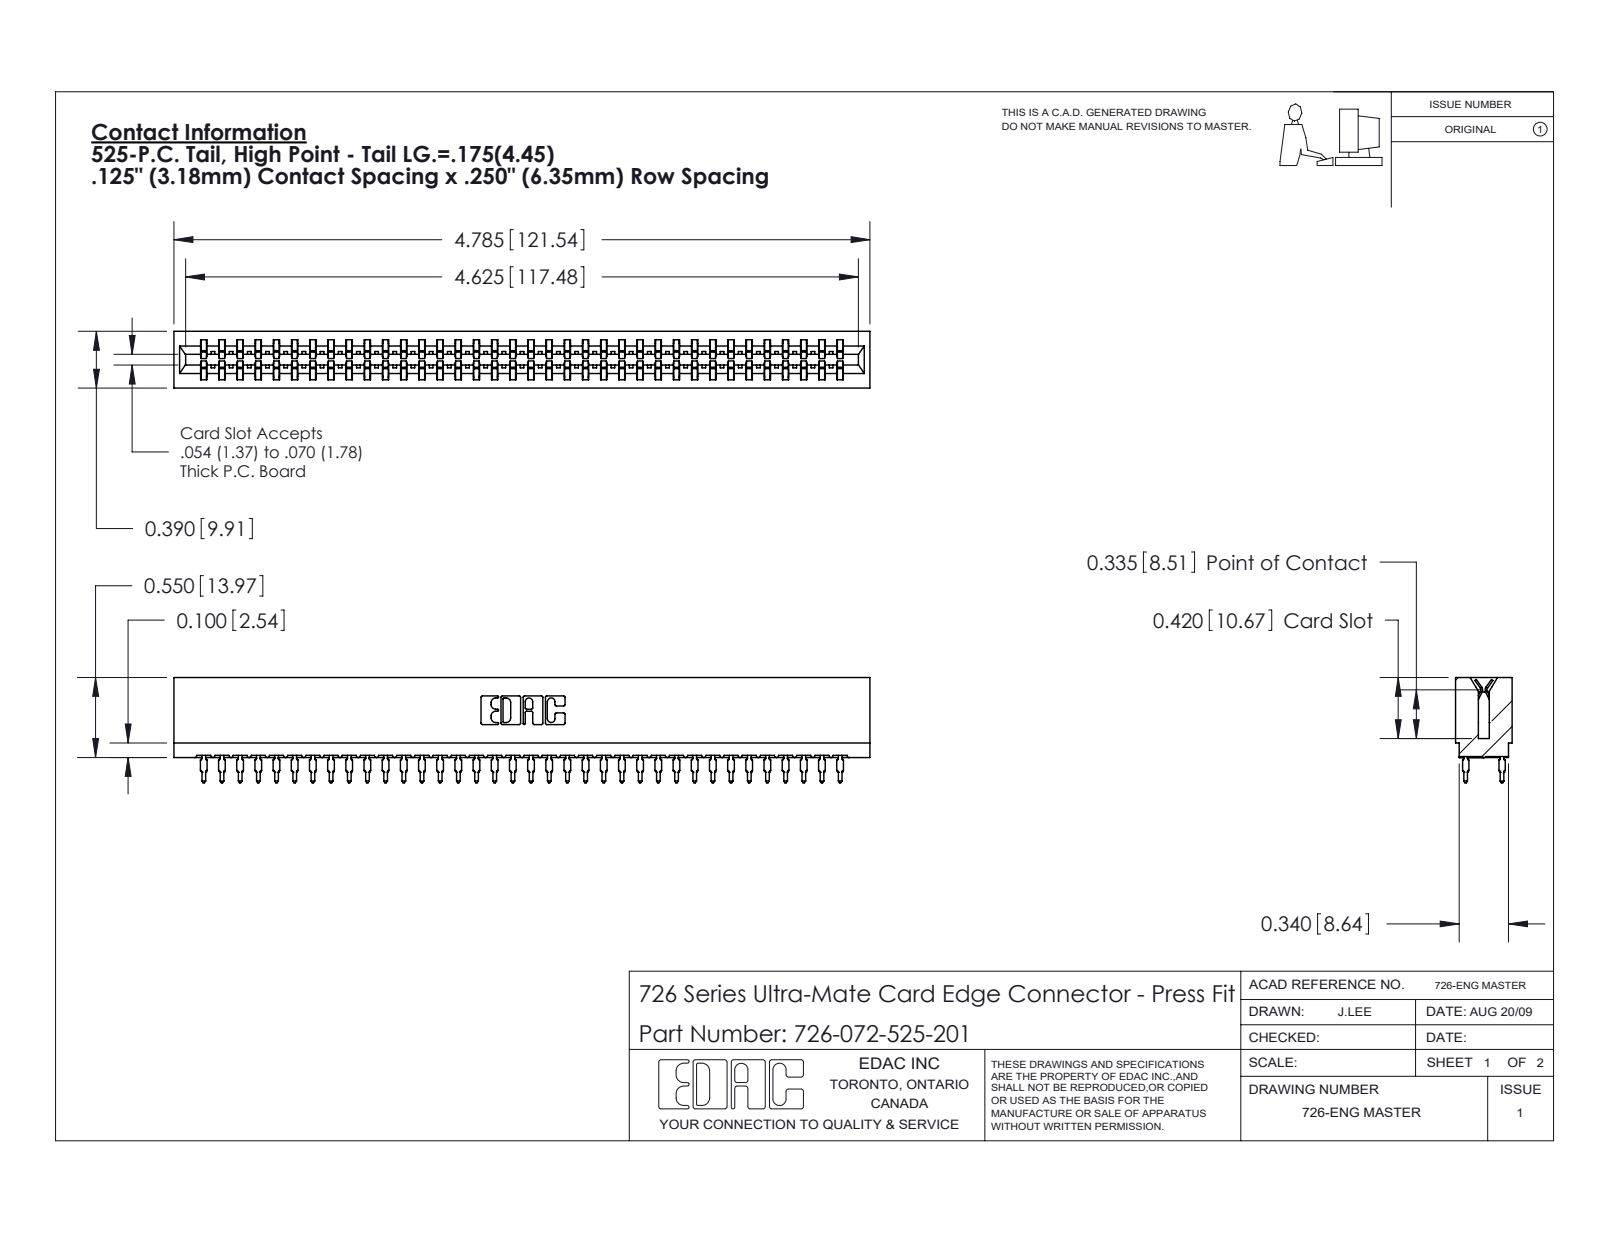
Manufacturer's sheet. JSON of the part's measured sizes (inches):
{"part_name": "726 Part_.515 Slot Depth - 01; 726-072-525-201; 746-292-001_525", "step_written_by": "SolidWorks 2020 (CONFIG_CONTROL_DESIGN)", "units": "inches", "bodies": {"solids": 73, "faces": 6541, "planar": 3367, "cylindrical": 1302, "other": 1872}, "overall_size": [4.785, 0.724, 0.39], "volume_in3": 0.682, "surface_area_in2": 28.46, "partial_cylinders_radius": [[0.021, 144], [0.015, 37], [0.01, 22], [0.005, 8], [0.011, 8], [0.007, 6], [0.031, 6], [0.026, 3]], "face_to_face_distances": [0.057, 0.333, 0.39, 0.025, 0.25, 0.307, 0.275, 0.083, 0.5, 0.365]}
